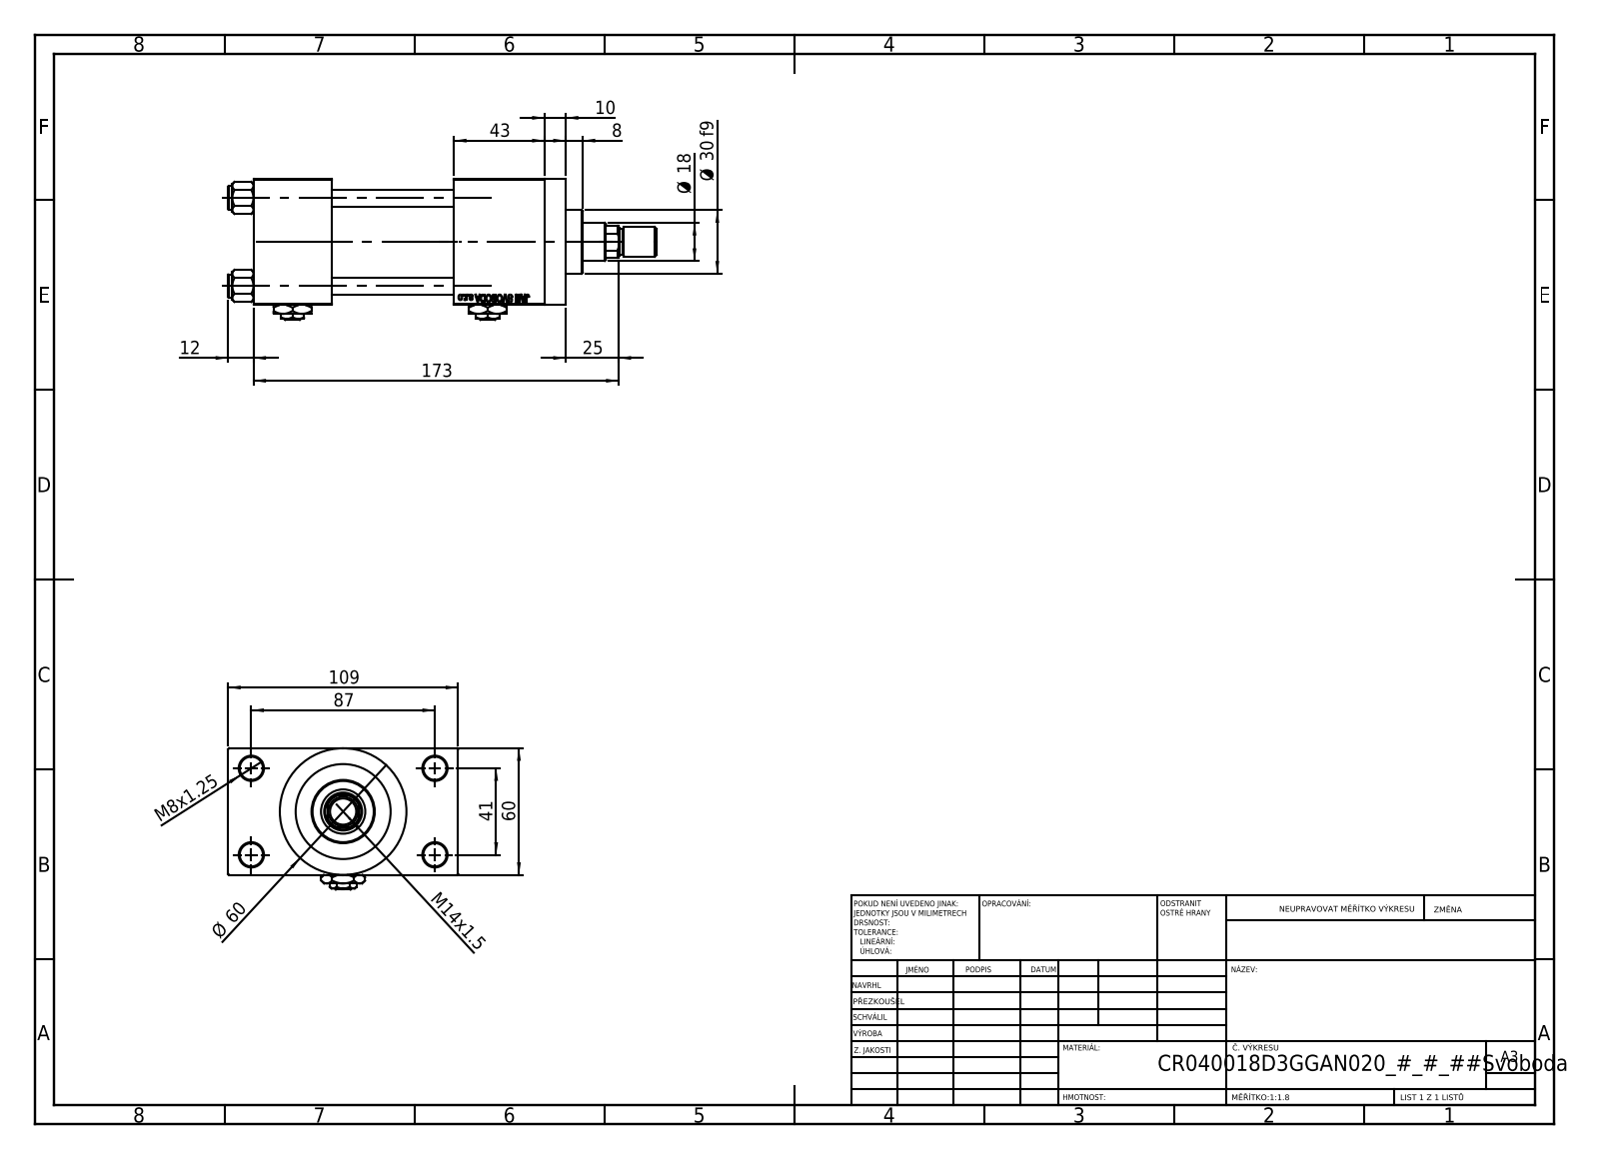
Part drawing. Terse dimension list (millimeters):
name: V215_VC_A; ROD_END_AH; V215CR_D_TYCINKA; NUT_M5_D (+3 more)
written by: SolidWorks 2019 (CONFIG_CONTROL_DESIGN)
unit: mm
bodies: 14 solids, 1220 faces (550 planar, 104 cylindrical, 566 other)
size: 203 × 109 × 67
volume: 518 264 mm³; area: 125 041 mm²
holes: 4× ⌀8, 4× ⌀11, 2× ⌀7, 2× ⌀16.66, 2× ⌀24, 1× ⌀8.5, 1× ⌀18, 1× ⌀21, 1× ⌀31, 1× ⌀40, 1× ⌀45
bosses: 4× ⌀11, 1× ⌀60, 1× ⌀46, 1× ⌀30, 1× ⌀14, 1× ⌀12
rounds: 1× R8.5
face distances: 60, 24.5, 84.5, 58, 37, 95, 43, 138, 101, 109
hole spacings: 22.65, 29.49, 41.7, 47.15, 48.09, 64.35, 76.49, 41
